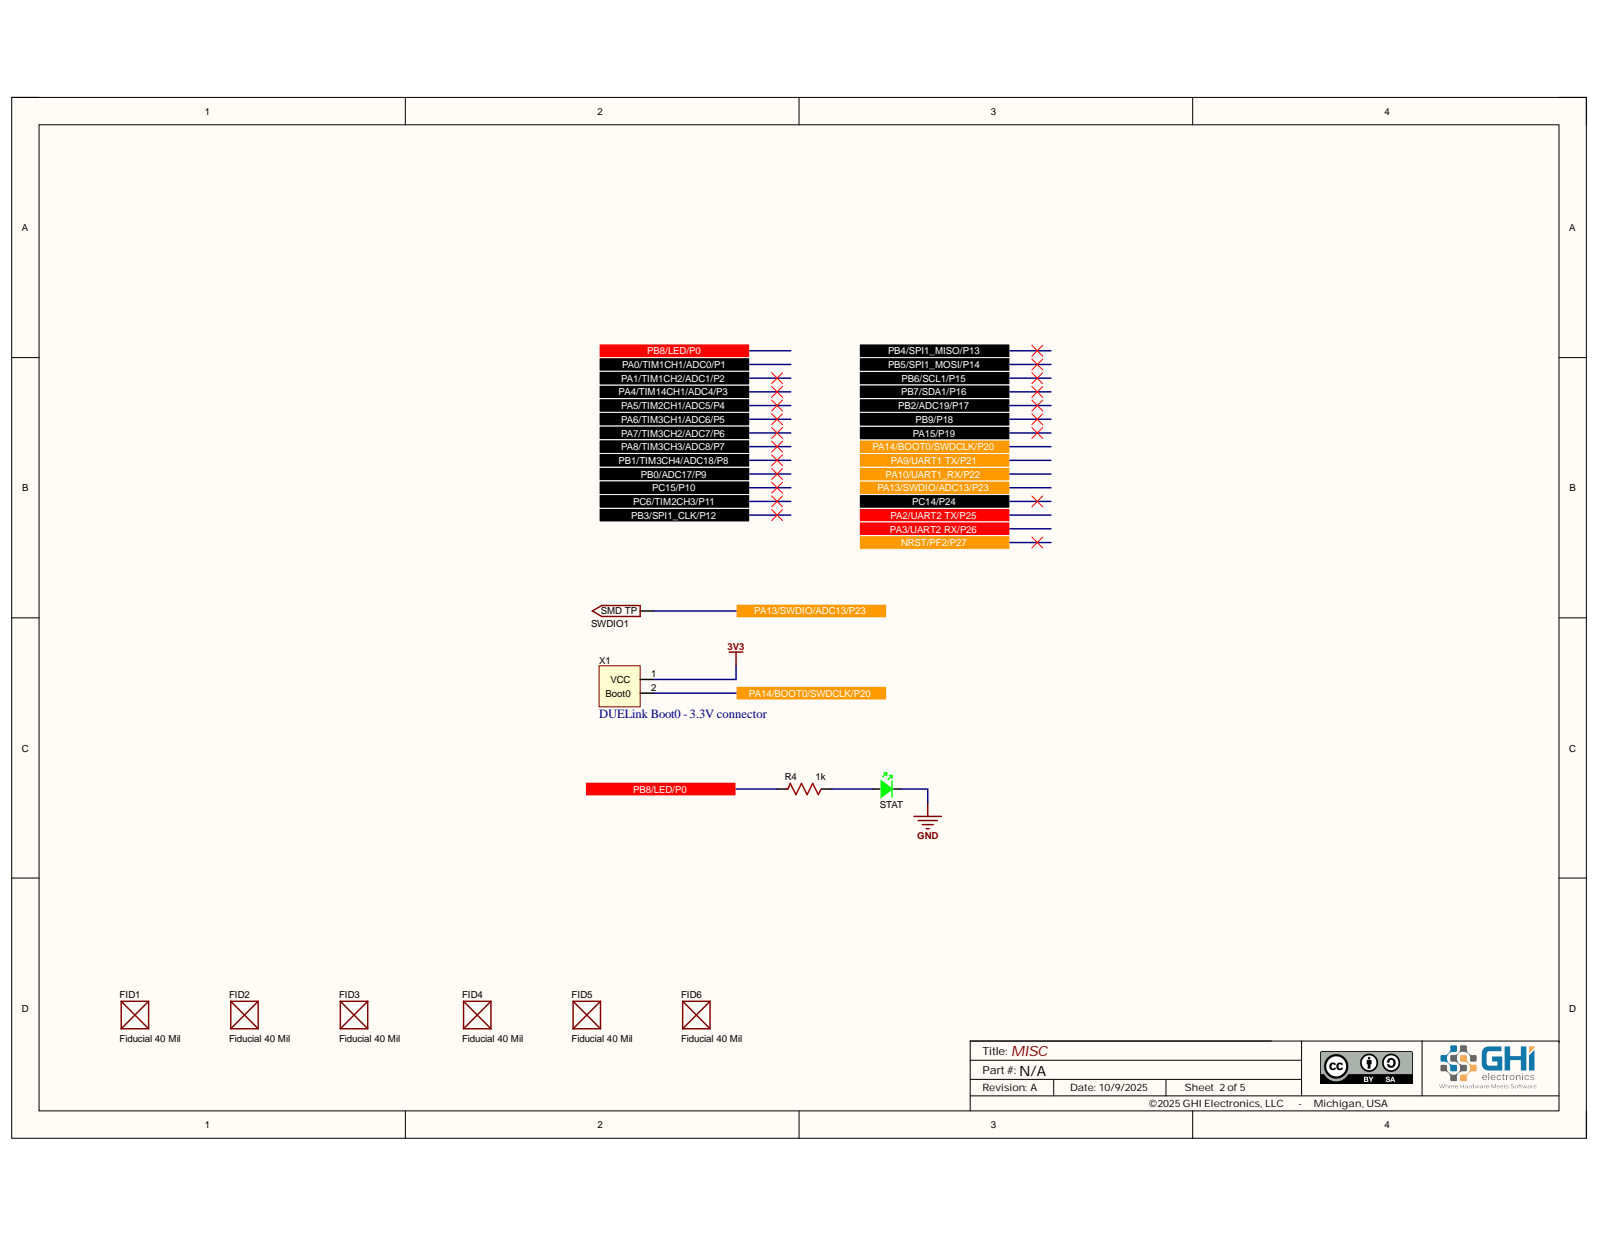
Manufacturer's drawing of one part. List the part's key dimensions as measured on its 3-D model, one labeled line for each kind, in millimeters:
Part name (STEP PRODUCT): PCB; Board; U2; 6433553952 (+7 more)
STEP written by: Open CASCADE 7.5 (AUTOMOTIVE_DESIGN)
Units: millimetres
Bodies: 80 solids, 1275 faces (971 planar, 204 cylindrical, 100 other)
Overall size (bounding box): 19 × 17 × 7.14
Volume: 566 mm³ · Surface area: 1 314 mm²
Round holes (diameter × count): ⌀1.02 ×2, ⌀3 ×2
Partial cylindrical surfaces — rounded edges, fillets, slot ends (radius × count): R0.12 ×35, R0.15 ×14, R0.17 ×2, R0.18 ×2, R0.18 ×2, R0.71 ×2, R1.5 ×2, R3.5 ×2
Main face-to-face distances: 1.6, 0.55, 1, 0.45, 2.53, 13.12, 16.45, 5, 1.85, 5.25
Hole centre spacings: 13.5, 2.54, 10, 16.03, 17.54
